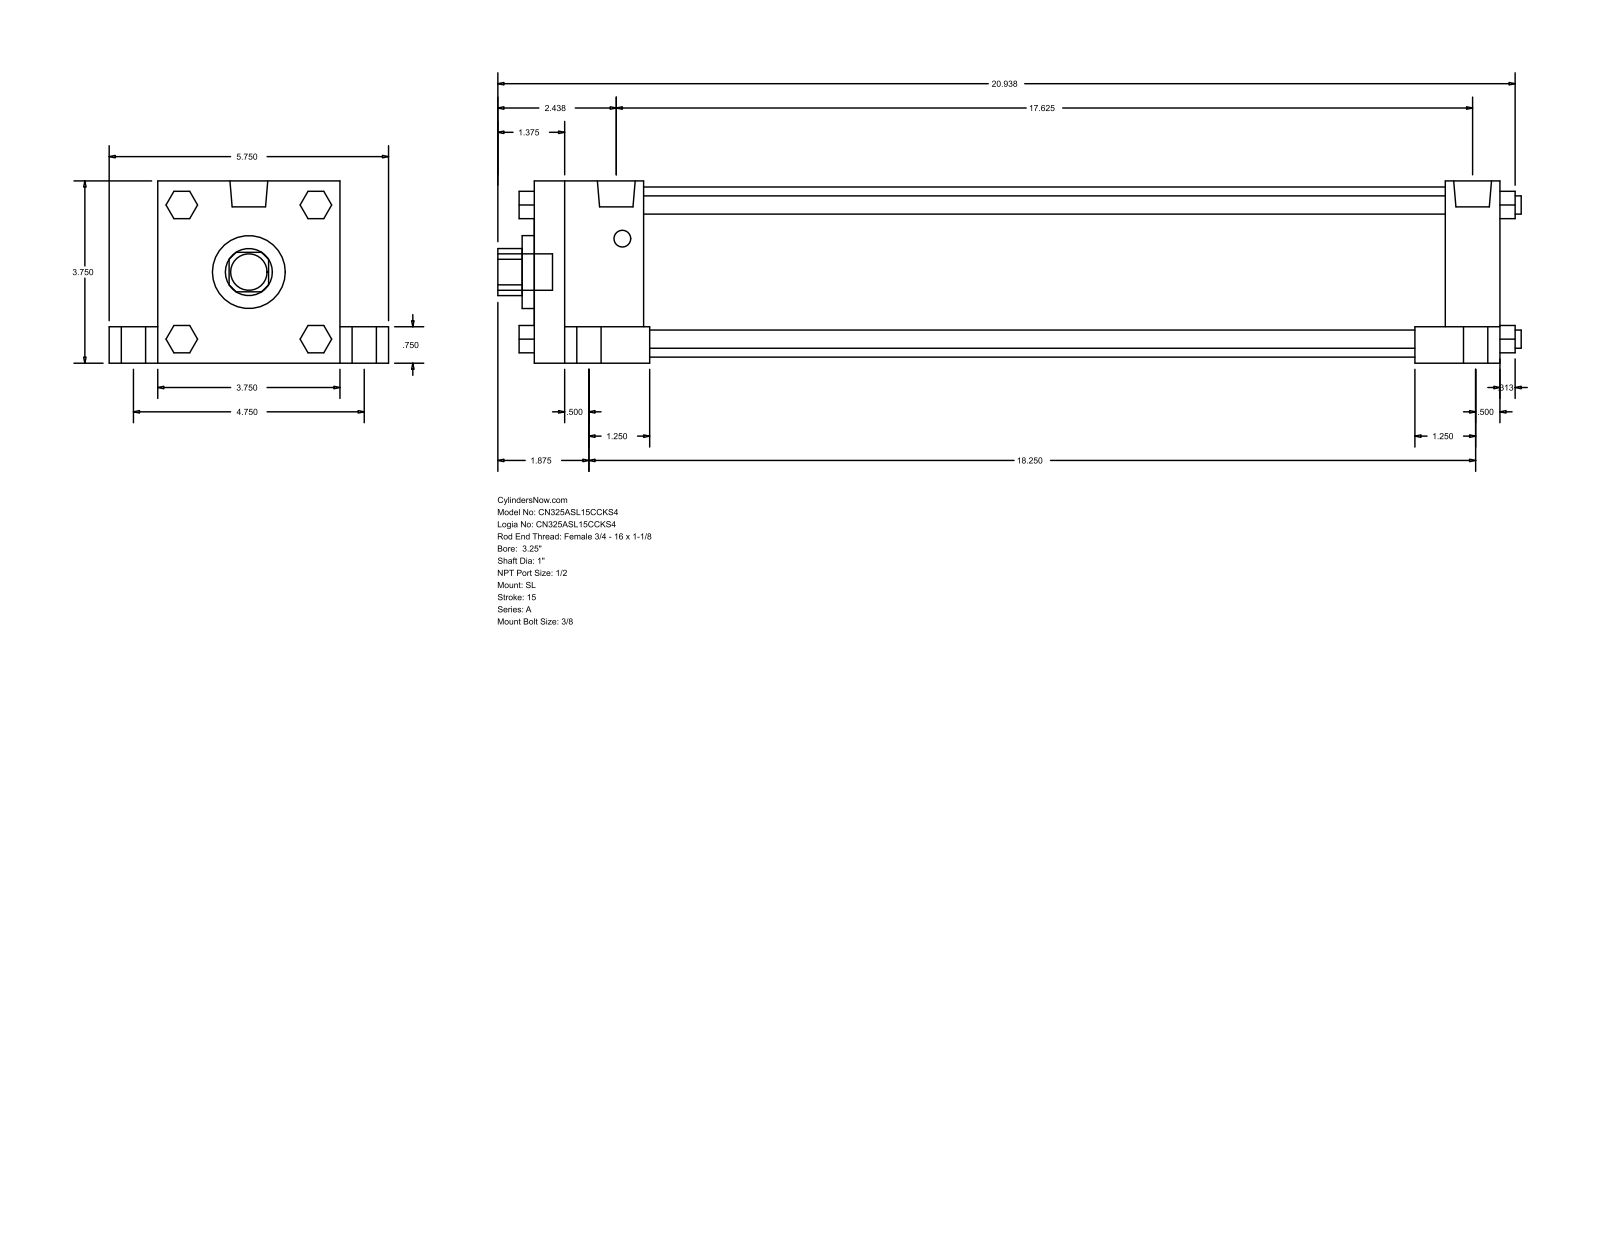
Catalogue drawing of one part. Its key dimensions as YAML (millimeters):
part_name: "A_SL__0325_1"
step_written_by: "GSSL Pune (CONFIG_CONTROL_DESIGN)"
units: millimeters
bodies: {solids: 0, faces: 150, planar: 114, cylindrical: 36, other: 0}
overall_size: [534.99, 146.05, 95.25]
round_holes:
  - {diameter: 25.4, count: 1}
  - {diameter: 38.1, count: 1}
  - {diameter: 88.9, count: 1}
round_bosses_or_shafts:
  - {diameter: 19.05, count: 5}
  - {diameter: 12.7, count: 4}
  - {diameter: 9.53, count: 4}
  - {diameter: 8.73, count: 4}
  - {diameter: 19.77, count: 2}
partial_cylinders:
  - {radius: 12.29, count: 1}
face_to_face_distances: [95.24, 504.83, 19.05, 25.41, 120.65, 76.19, 15.87, 57.15, 476.25, 419.1]
